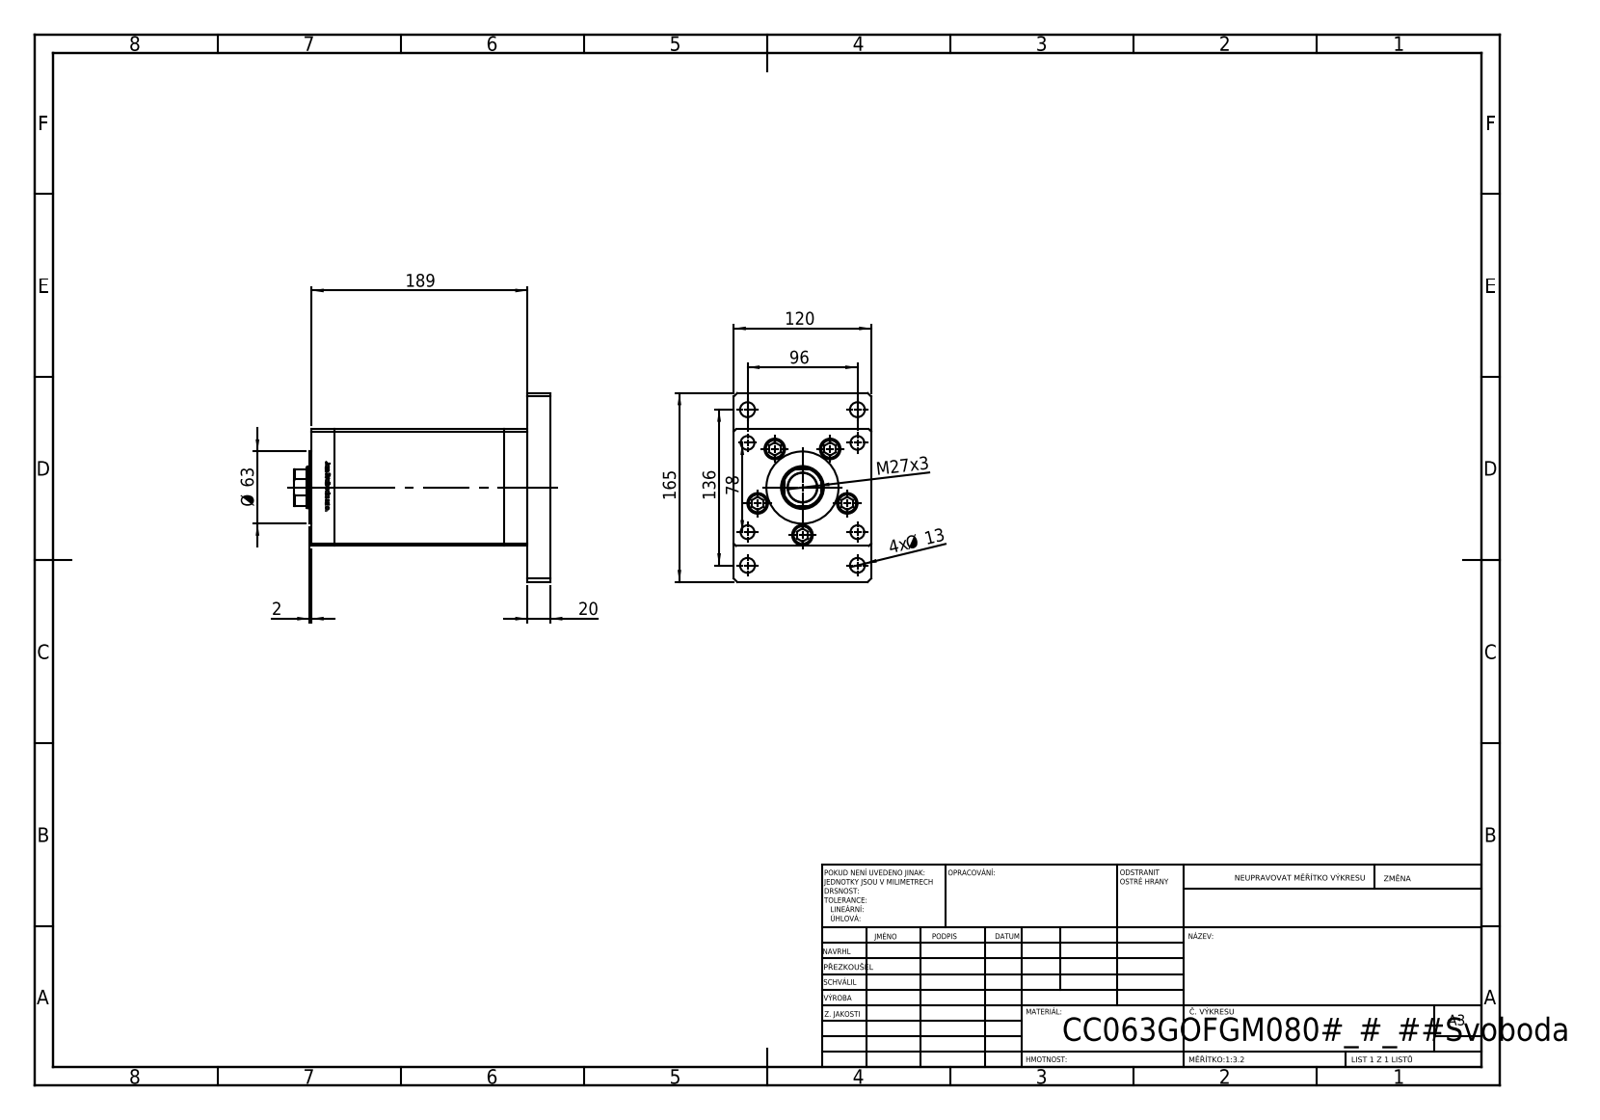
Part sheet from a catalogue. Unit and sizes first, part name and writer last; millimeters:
Units: millimetres
Overall size (bounding box): 223.5 × 165 × 120
Round holes (diameter × count): ⌀12 ×9, ⌀13.5 ×5, ⌀18 ×5, ⌀13 ×4, ⌀17 ×4, ⌀25.5 ×1, ⌀36 ×1, ⌀37.5 ×1, ⌀83 ×1
Round bosses / shafts (diameter × count): ⌀8 ×9, ⌀17 ×5, ⌀63 ×1
Partial cylindrical surfaces — rounded edges, fillets, slot ends (radius × count): R0.93 ×2, R17.5 ×1
Main face-to-face distances: 20, 168.5, 120, 188.5, 102, 148.5, 40, 2, 186.5, 18
Hole centre spacings: 41.5, 29, 61.85, 83.23, 96, 100.28, 107, 143.75
Volume: 2 398 000 mm³ · Surface area: 317 156 mm²
Bodies: 19 solids, 1301 faces (514 planar, 181 cylindrical, 606 other)
Part name (STEP PRODUCT): V220C_FRONT_G; ALLEN BOLT; V220C BACK_G; V220C_G_MIDDLE (+2 more)
STEP written by: SolidWorks 2019 (CONFIG_CONTROL_DESIGN)
